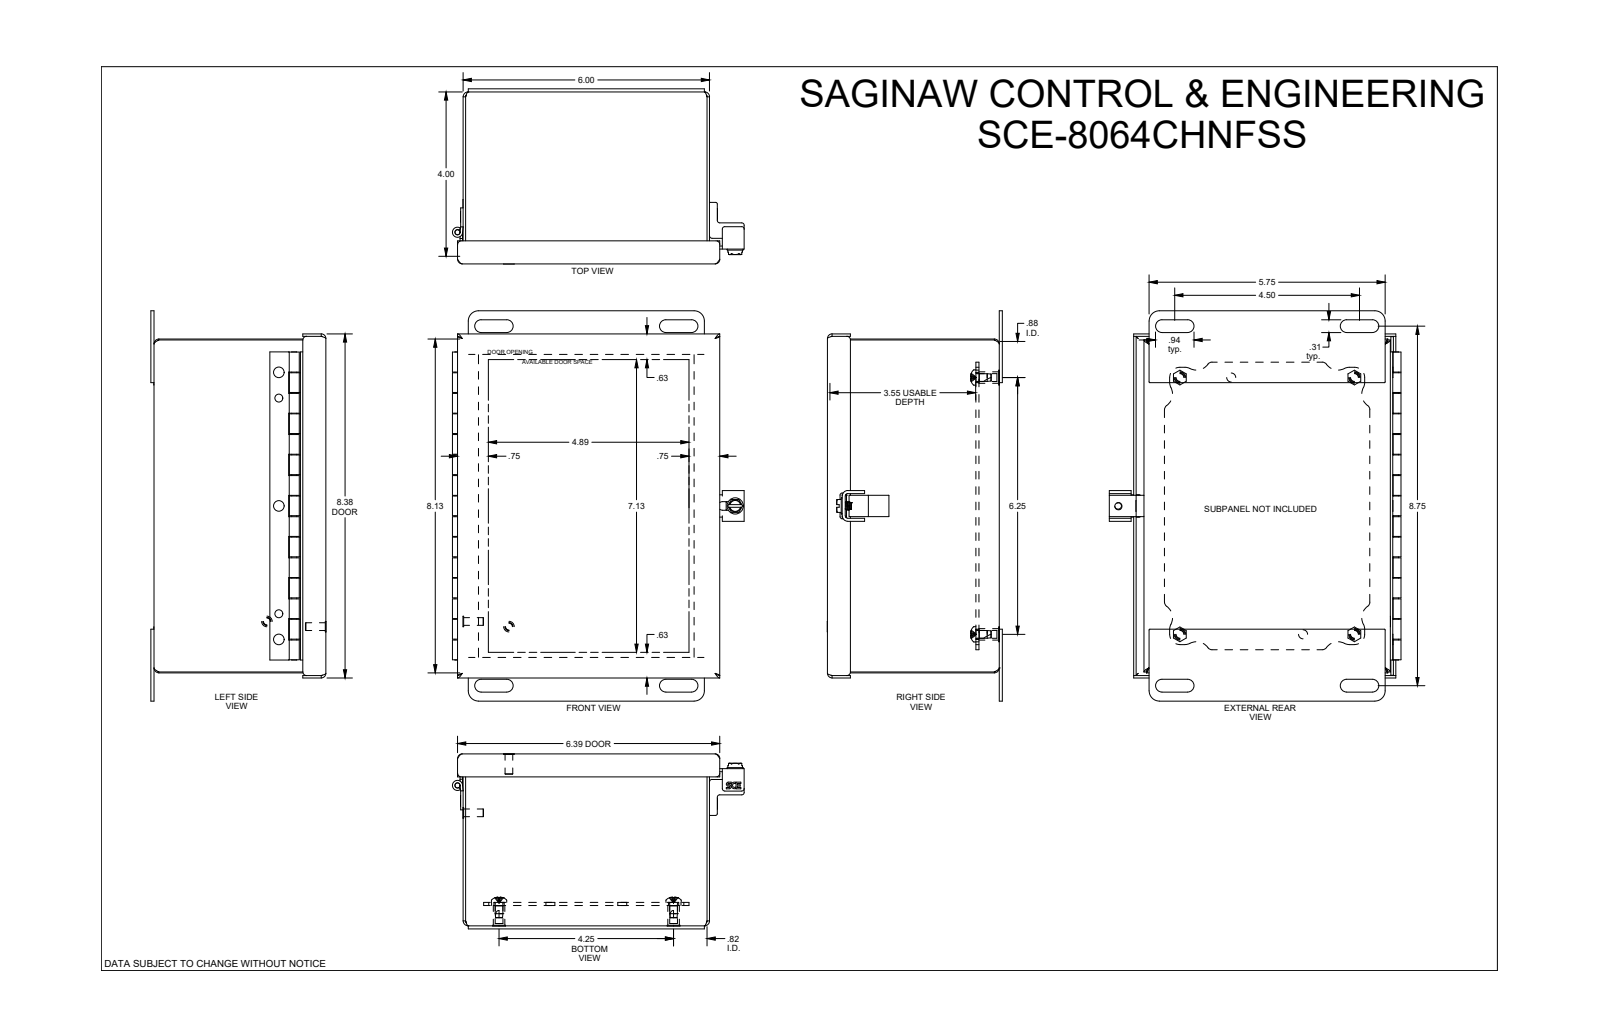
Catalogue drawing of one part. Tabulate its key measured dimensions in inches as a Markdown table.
| quantity | value |
| --- | --- |
| part name | SCE-8064CHNFSS |
| STEP written by | SolidWorks 2019 (CONFIG_CONTROL_DESIGN) |
| units | inches |
| bodies | 0 solids, 1097 faces (504 planar, 295 cylindrical, 298 other) |
| overall size | 9.5 × 7.104 × 4.265 |
| round holes (diameter × count) | 0.19 × 8, 0.193 × 6, 0.25 × 4, 0.281 × 4, 0.193 × 2, 0.218 × 2, 0.126 × 1, 0.156 × 1, 0.266 × 1 |
| round bosses / shafts (diameter × count) | 0.188 × 11, 0.256 × 6, 0.373 × 4, 0.28 × 4, 0.396 × 1, 0.246 × 1, 0.123 × 1 |
| partial cylindrical surfaces (radius × count) | 0.01 × 48, 0.06 × 17, 0.25 × 16, 0.007 × 8, 0.052 × 8, 0.112 × 8, 0.125 × 8, 0.156 × 8 |
| main face-to-face distances | 0.06, 0.06, 5.94, 4.125, 4.185, 4.065, 4.125, 0.075, 6, 3.63 |
| hole center spacings | 1.25, 3, 3.25, 3.251, 4.25, 6.25, 6.374, 6.933 |
